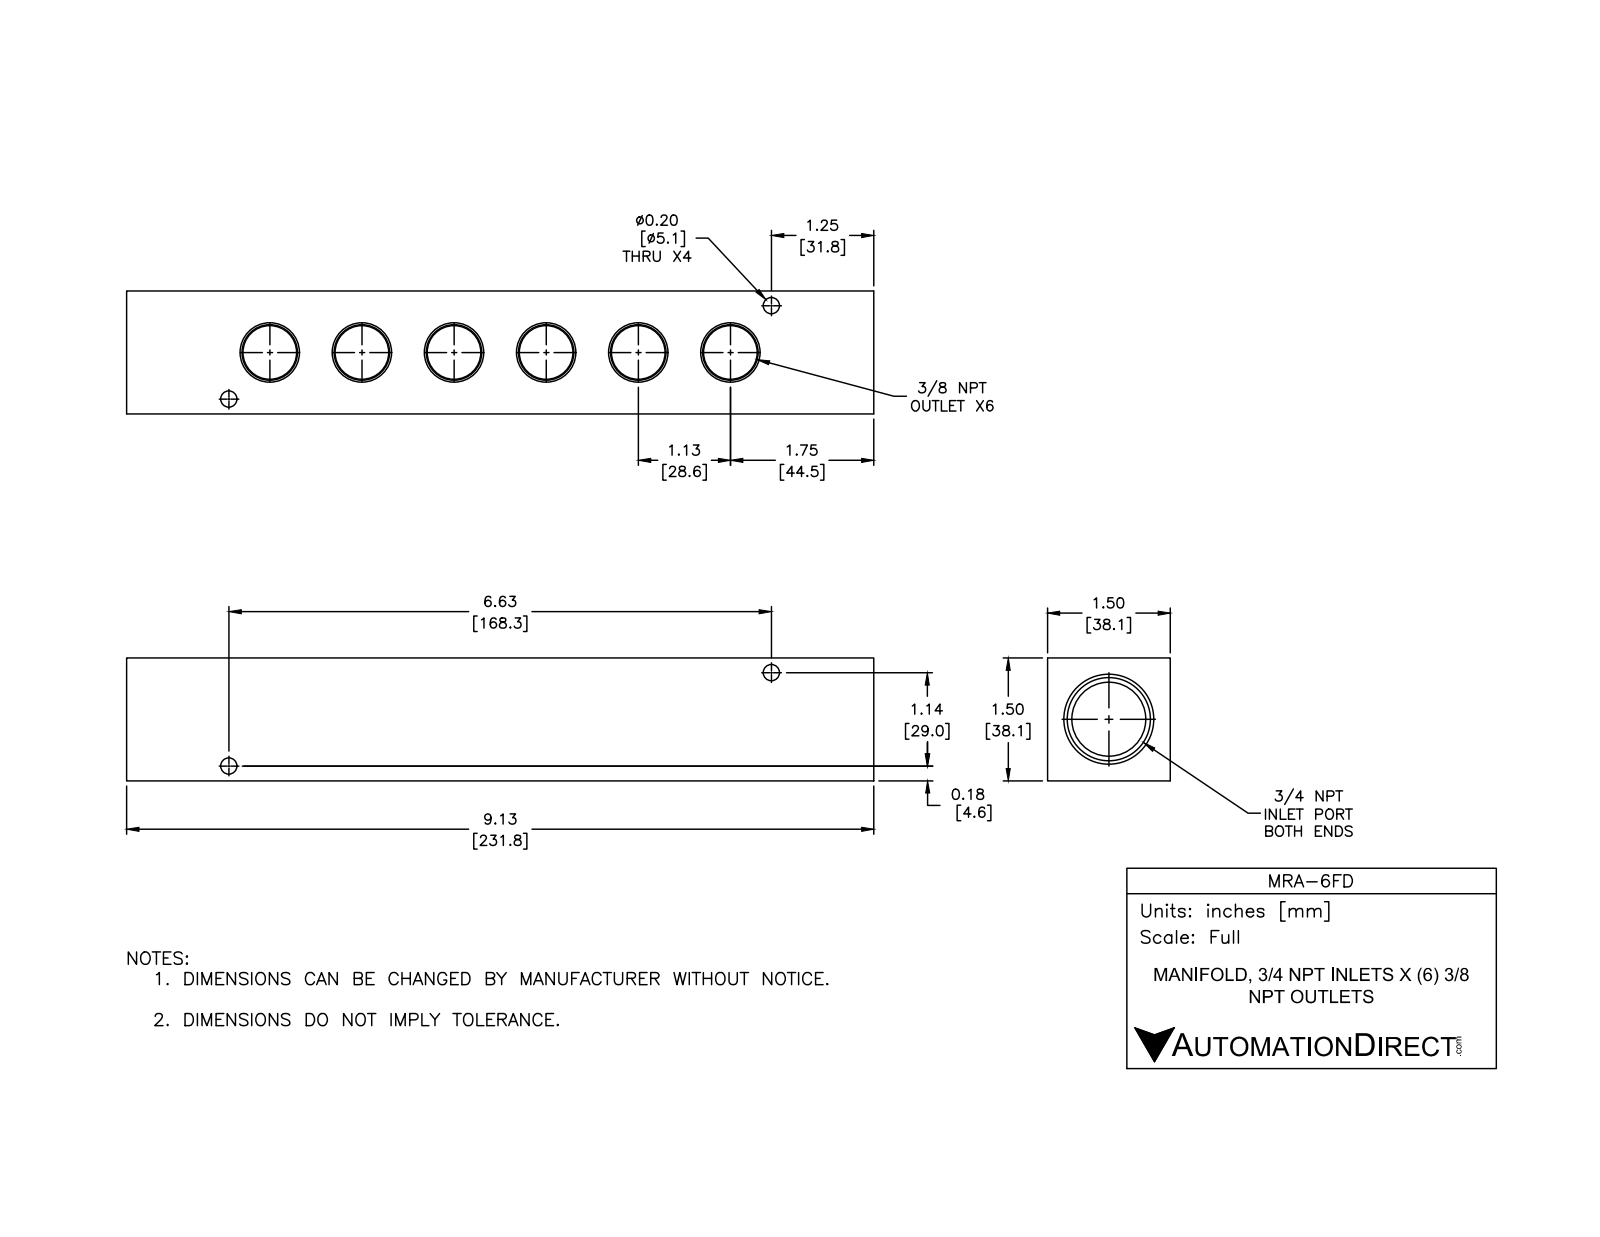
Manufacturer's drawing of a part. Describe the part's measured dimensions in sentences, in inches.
The part is named "MRA-6FD". Its 3-D file was written by "SolidWorks 2015 (CONFIG_CONTROL_DESIGN)". It is 1 solid with 70 faces: 20 planar, 18 cylindrical and 32 other. Overall it measures 9.125 by 1.5 by 1.5 inches. Its volume is 13.56 cubic inches and its surface area 87.5 square inches. Round holes: 4 of diameter 0.2, 1 of diameter 0.906. The main face-to-face distances are 1.5, 9.125, 0.55, 8.575, 8.025, 1.09, 0.41. The hole center spacings are 6.722.
